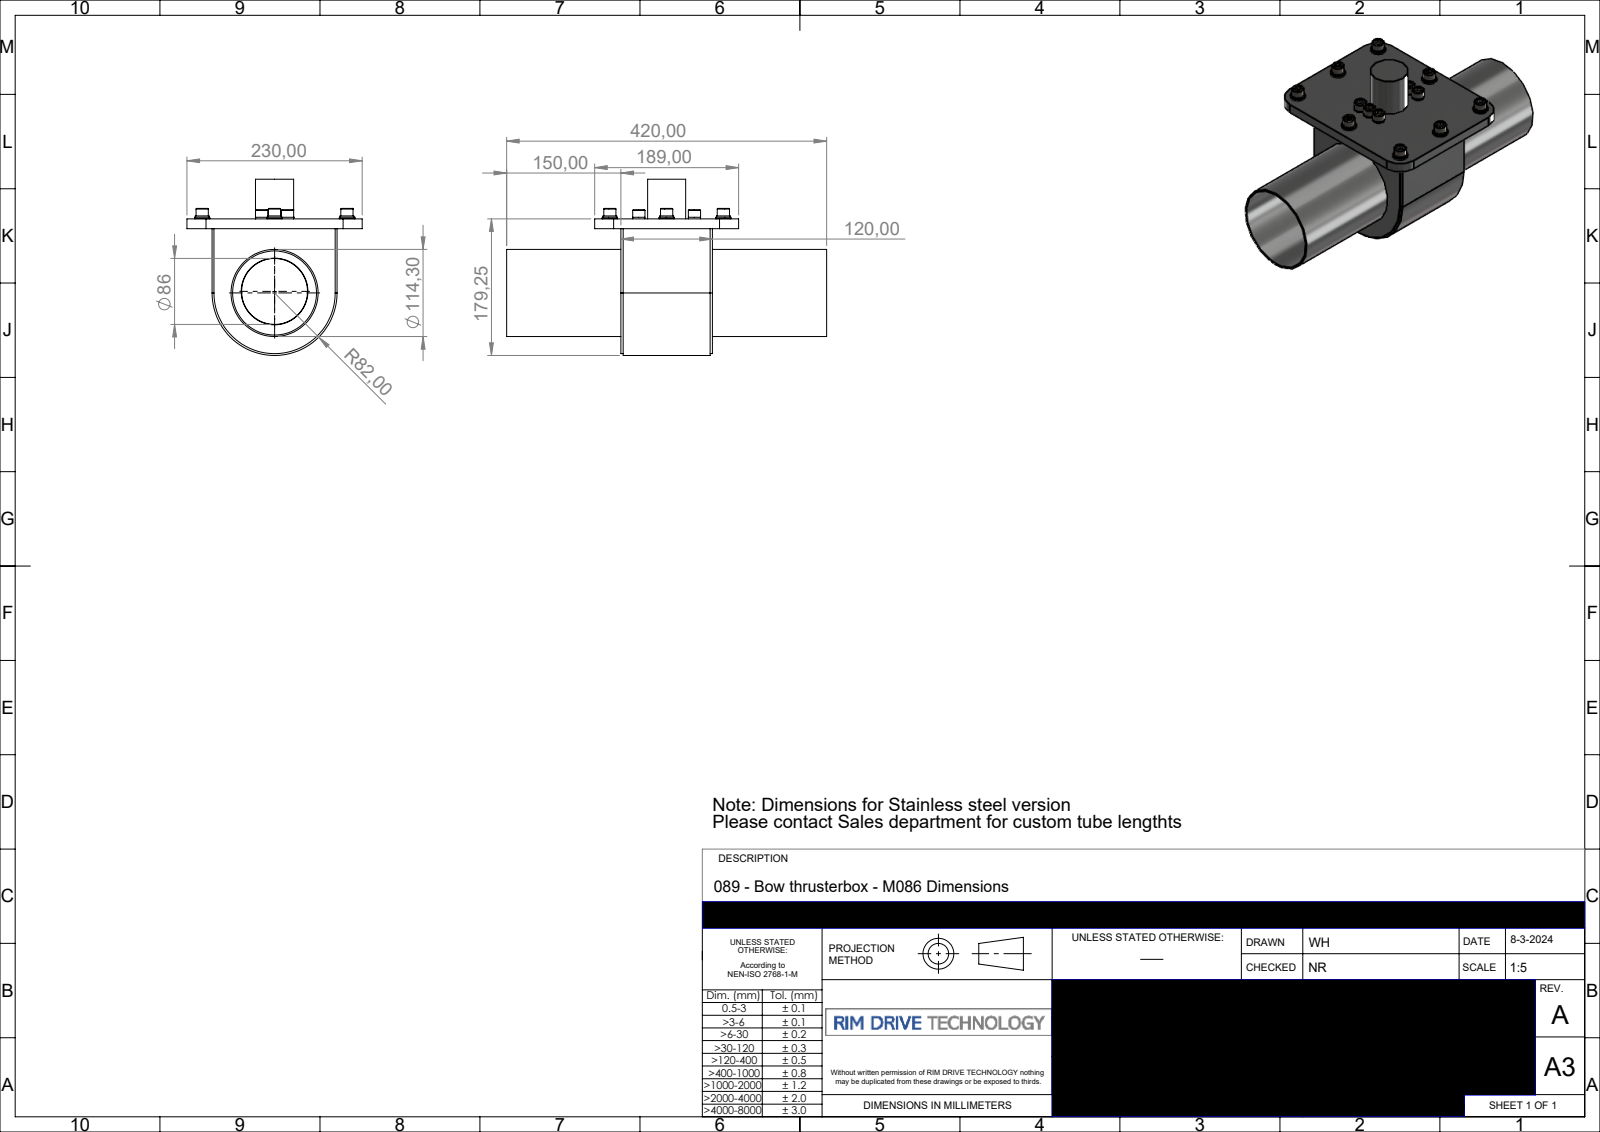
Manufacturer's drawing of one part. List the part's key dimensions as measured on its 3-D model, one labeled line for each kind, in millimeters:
Part name (STEP PRODUCT): P-089-030-rev-A-M086
STEP written by: SolidWorks 2023 (AUTOMOTIVE_DESIGN)
Units: millimetres
Bodies: 1 solid, 574 faces (292 planar, 160 cylindrical, 122 other)
Overall size (bounding box): 420 × 231.25 × 230
Volume: 3 104 000 mm³ · Surface area: 432 074 mm²
Round holes (diameter × count): ⌀10.2 ×8, ⌀10.5 ×8, ⌀10.35 ×6, ⌀86.5 ×1, ⌀87.5 ×1, ⌀110.3 ×1
Round bosses / shafts (diameter × count): ⌀16 ×14, ⌀10 ×14, ⌀20 ×8, ⌀18.1 ×8, ⌀15.88 ×6, ⌀114.3 ×1, ⌀50 ×1
Partial cylindrical surfaces — rounded edges, fillets, slot ends (radius × count): R25 ×4, R79.5 ×1, R82 ×1
Main face-to-face distances: 13, 120, 164, 34.5, 154.5, 33, 197, 189, 37.5, 151.5
Hole centre spacings: 17, 41.63, 74.5, 74.95, 86.12, 86.76, 95, 101.77
